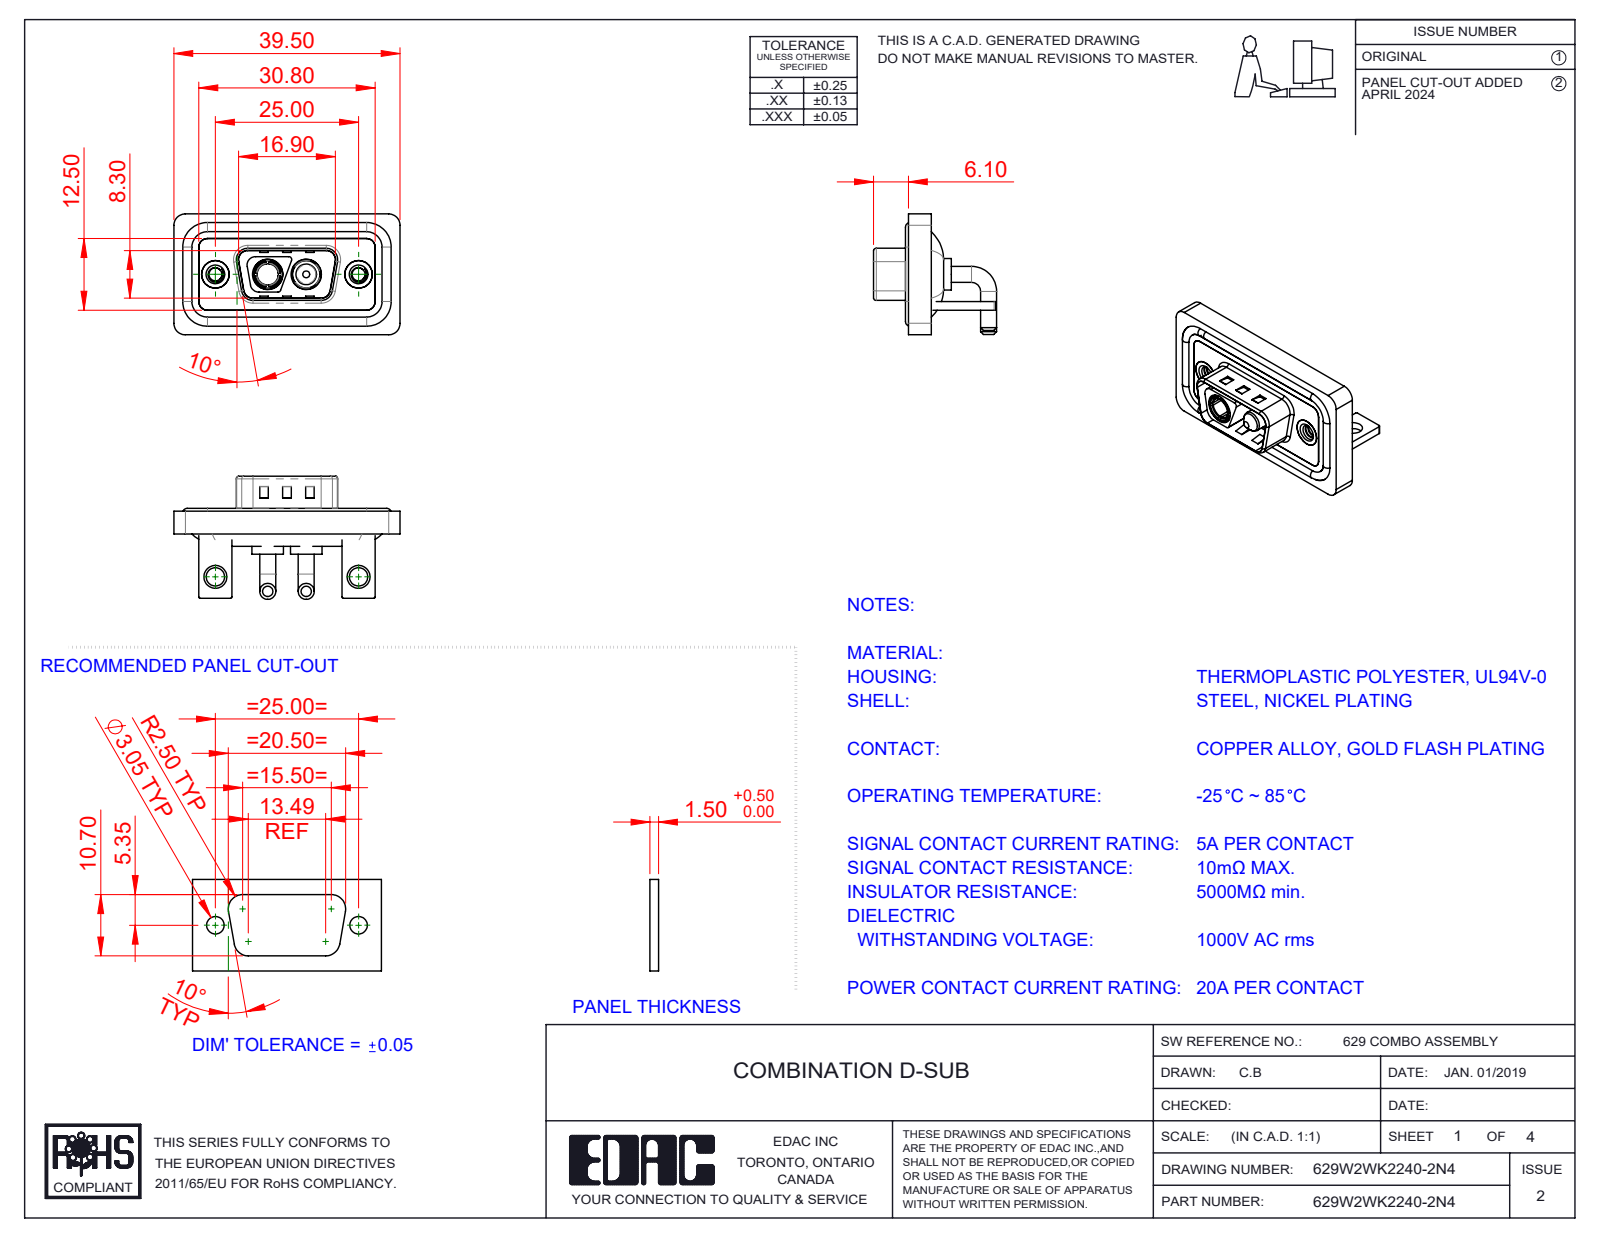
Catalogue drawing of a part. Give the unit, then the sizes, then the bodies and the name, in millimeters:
Units: millimetres
Overall size (bounding box): 39.5 × 21.5 × 21.1
Round holes (diameter × count): ⌀2.26 ×2, ⌀3.2 ×2, ⌀4 ×2, ⌀4.8 ×2, ⌀4.85 ×2, ⌀5 ×2, ⌀5.3 ×2, ⌀3.7 ×1
Round bosses / shafts (diameter × count): ⌀2.8 ×4, ⌀1.6 ×4, ⌀5.5 ×2, ⌀5.2 ×2, ⌀4.9 ×2, ⌀4.75 ×2, ⌀3.75 ×2, ⌀4.96 ×1
Partial cylindrical surfaces — rounded edges, fillets, slot ends (radius × count): R1.5 ×20, R2 ×19, R0.25 ×16, R0.5 ×11, R1.6 ×8, R0.6 ×4, R0.65 ×4, R0.9 ×4
Main face-to-face distances: 0.4, 1.5, 2.9, 0.8, 1.1, 1.2, 2.1, 1.6, 3.7, 2.5
Hole centre spacings: 9.14, 15.86, 25, 6.72
Volume: 4 960 mm³ · Surface area: 8 119 mm²
Bodies: 13 solids, 582 faces (209 planar, 249 cylindrical, 124 other)
Part name (STEP PRODUCT): 629Combo Housing_2WK2; 629Combo Threaded Rivet_3; 629Combo Shell Front_09 Contacts; 629W2WK2140-2N4 (+5 more)
STEP written by: SolidWorks 2023 (CONFIG_CONTROL_DESIGN)
